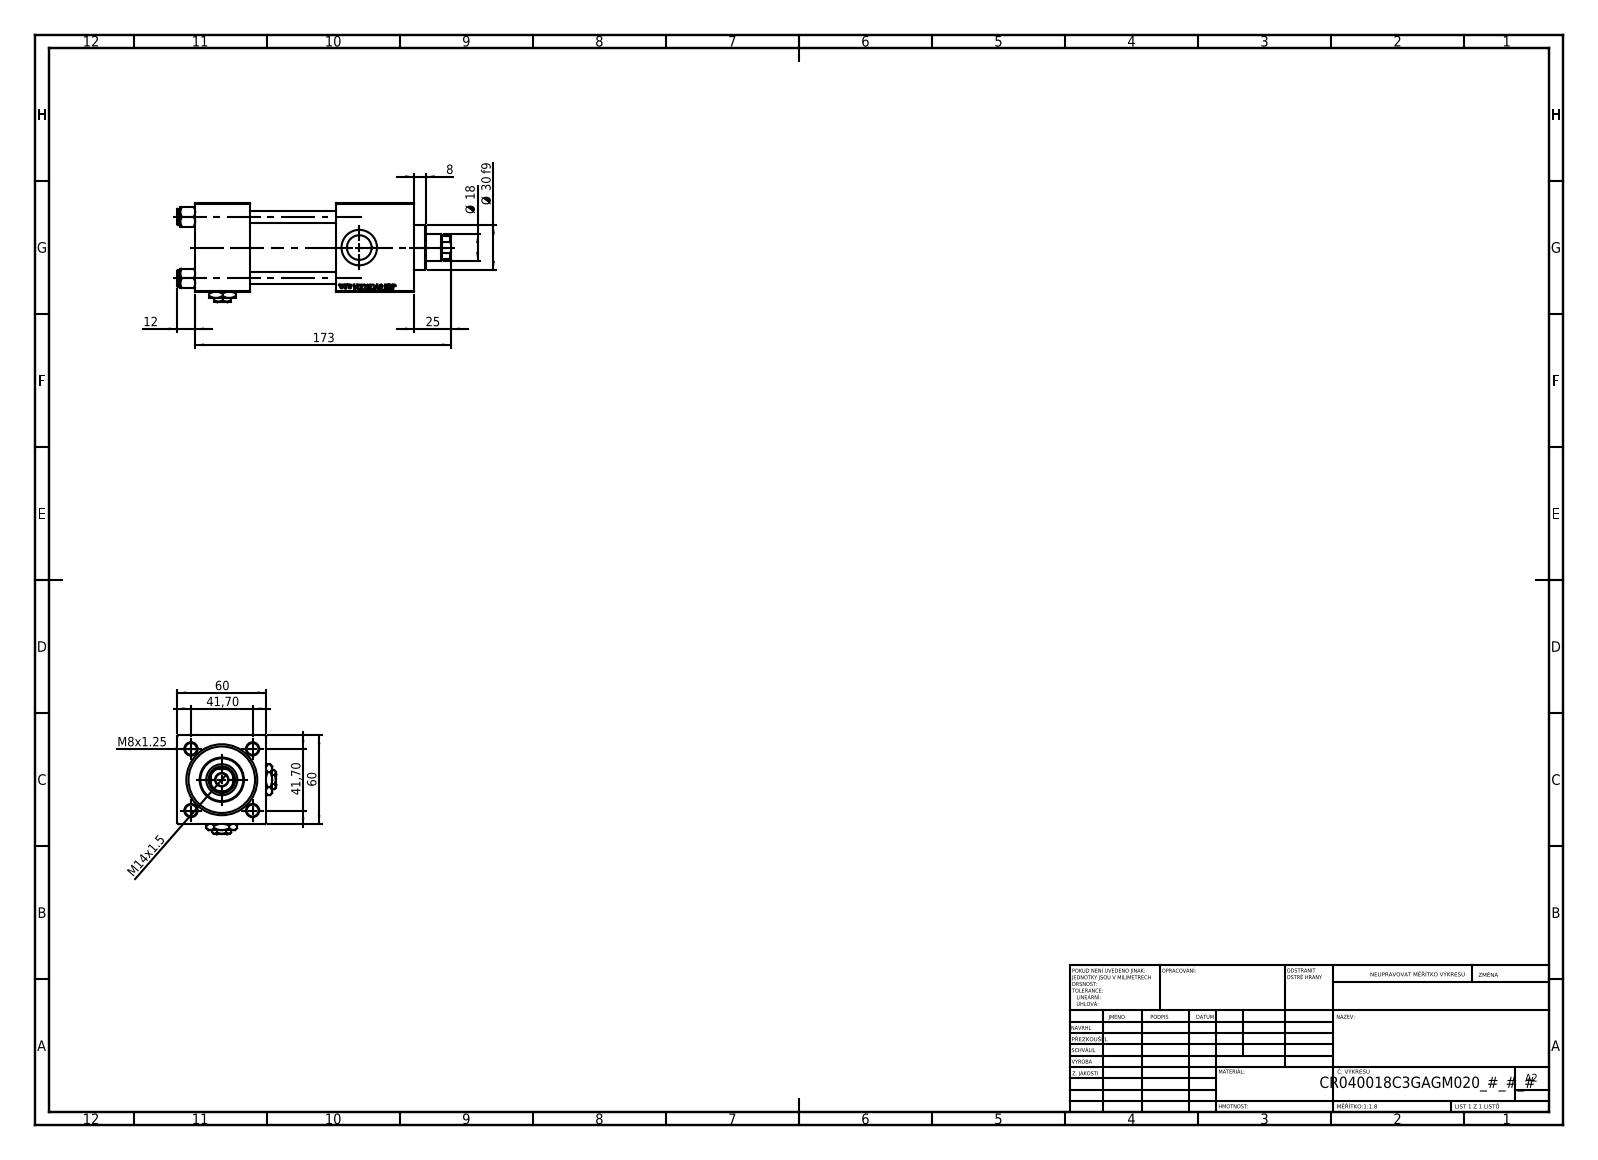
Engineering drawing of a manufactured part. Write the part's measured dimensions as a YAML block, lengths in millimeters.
part_name: "V215CR_C_TYCINKA; V215CR_C_Body; V215_VC_A; NUT_M5_C (+2 more)"
step_written_by: "SolidWorks 2019 (CONFIG_CONTROL_DESIGN)"
units: millimeters
bodies: {solids: 13, faces: 1250, planar: 574, cylindrical: 98, other: 578}
overall_size: [185, 67, 67]
volume: 398841
surface_area: 108335
round_holes:
  - {diameter: 8, count: 4}
  - {diameter: 7, count: 2}
  - {diameter: 16.66, count: 2}
  - {diameter: 24, count: 2}
  - {diameter: 8.5, count: 1}
  - {diameter: 18, count: 1}
  - {diameter: 21, count: 1}
  - {diameter: 31, count: 1}
  - {diameter: 40, count: 1}
  - {diameter: 45, count: 1}
round_bosses_or_shafts:
  - {diameter: 11, count: 4}
  - {diameter: 46, count: 1}
  - {diameter: 30, count: 1}
partial_cylinders:
  - {radius: 8.5, count: 1}
face_to_face_distances: [60, 37, 53, 148, 111, 58, 95, 119.3, 82.3, 24.3]
hole_center_spacings: [29.49, 41.7, 58.97]
